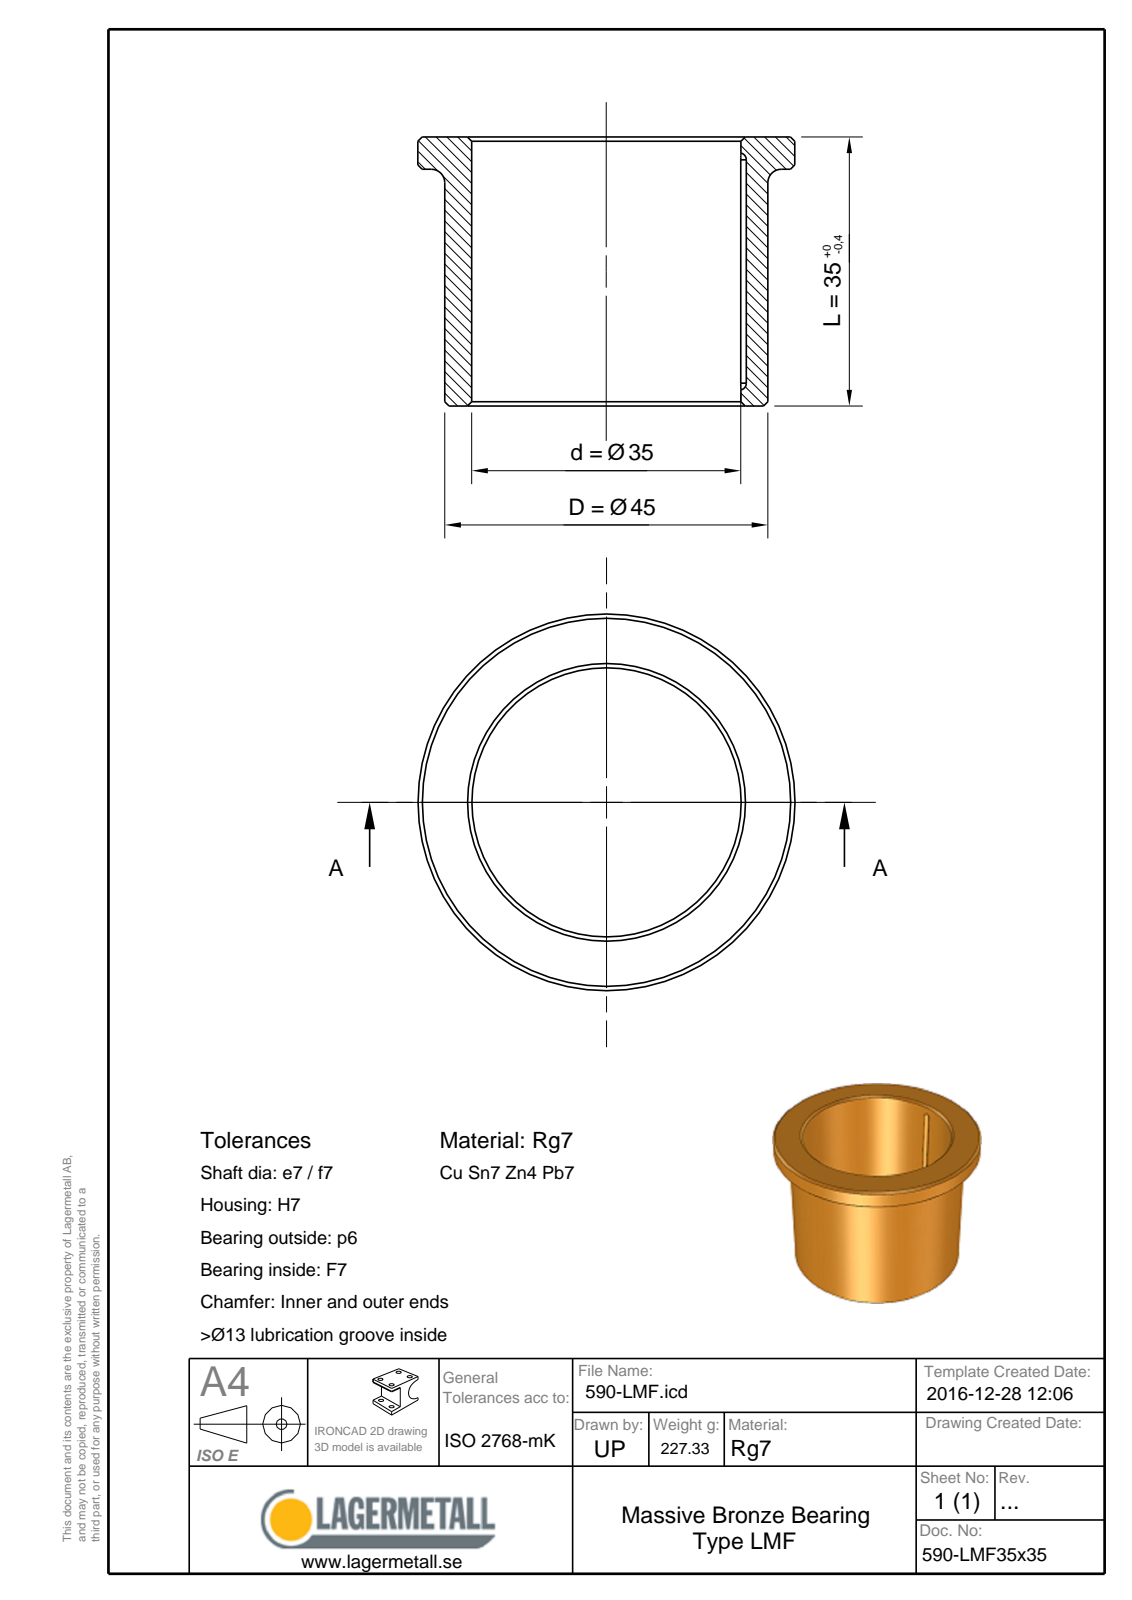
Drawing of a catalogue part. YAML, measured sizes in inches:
part_name: "590-LMF35x35"
step_written_by: "Spatial InterOp 3D (CONFIG_CONTROL_DESIGN)"
units: inches
bodies: {solids: 1, faces: 17, planar: 4, cylindrical: 5, other: 8}
overall_size: [2.165, 2.165, 1.378]
volume: 1.576
surface_area: 17.56
round_holes:
  - {diameter: 1.378, count: 1}
round_bosses_or_shafts:
  - {diameter: 2.165, count: 1}
  - {diameter: 1.772, count: 1}
partial_cylinders:
  - {radius: 0.049, count: 2}
face_to_face_distances: [1.378, 1.181, 0.197]
